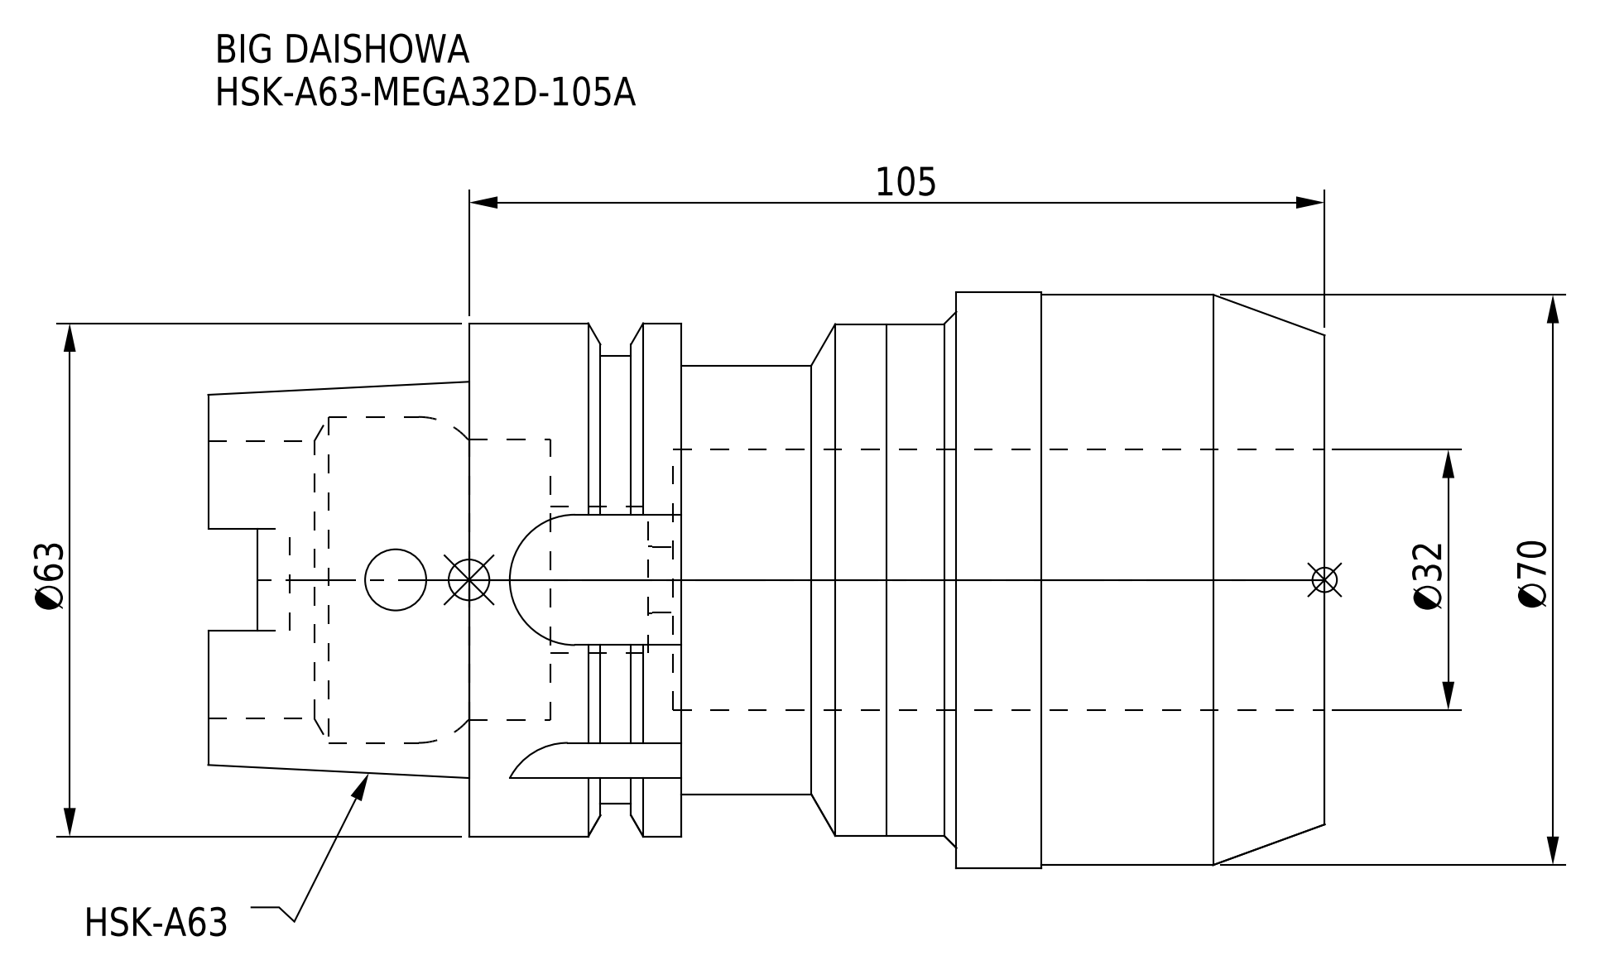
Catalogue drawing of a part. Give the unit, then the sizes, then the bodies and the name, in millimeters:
Units: millimetres
Overall size (bounding box): 137 × 70.7 × 70.7
Round holes (diameter × count): ⌀7.5 ×1, ⌀8 ×1, ⌀8.2 ×1, ⌀18 ×1, ⌀32 ×1, ⌀34 ×1, ⌀34.5 ×1, ⌀40 ×1
Round bosses / shafts (diameter × count): ⌀70.7 ×1, ⌀70 ×1, ⌀63 ×1, ⌀62.8 ×1, ⌀55 ×1, ⌀52.6 ×1
Partial cylindrical surfaces — rounded edges, fillets, slot ends (radius × count): R2.88 ×4, R8 ×4
Main face-to-face distances: 105, 26, 1, 79, 80, 25, 95.05, 16.05, 15.05, 9.95
Volume: 273 656 mm³ · Surface area: 48 298 mm²
Bodies: 1 solid, 103 faces (40 planar, 43 cylindrical, 20 other)
Part name (STEP PRODUCT): HSK-A63-MEGA32D-105A
STEP written by: CREO PARAMETRIC BY PTC INC, 2016380 (AUTOMOTIVE_DESIGN)
